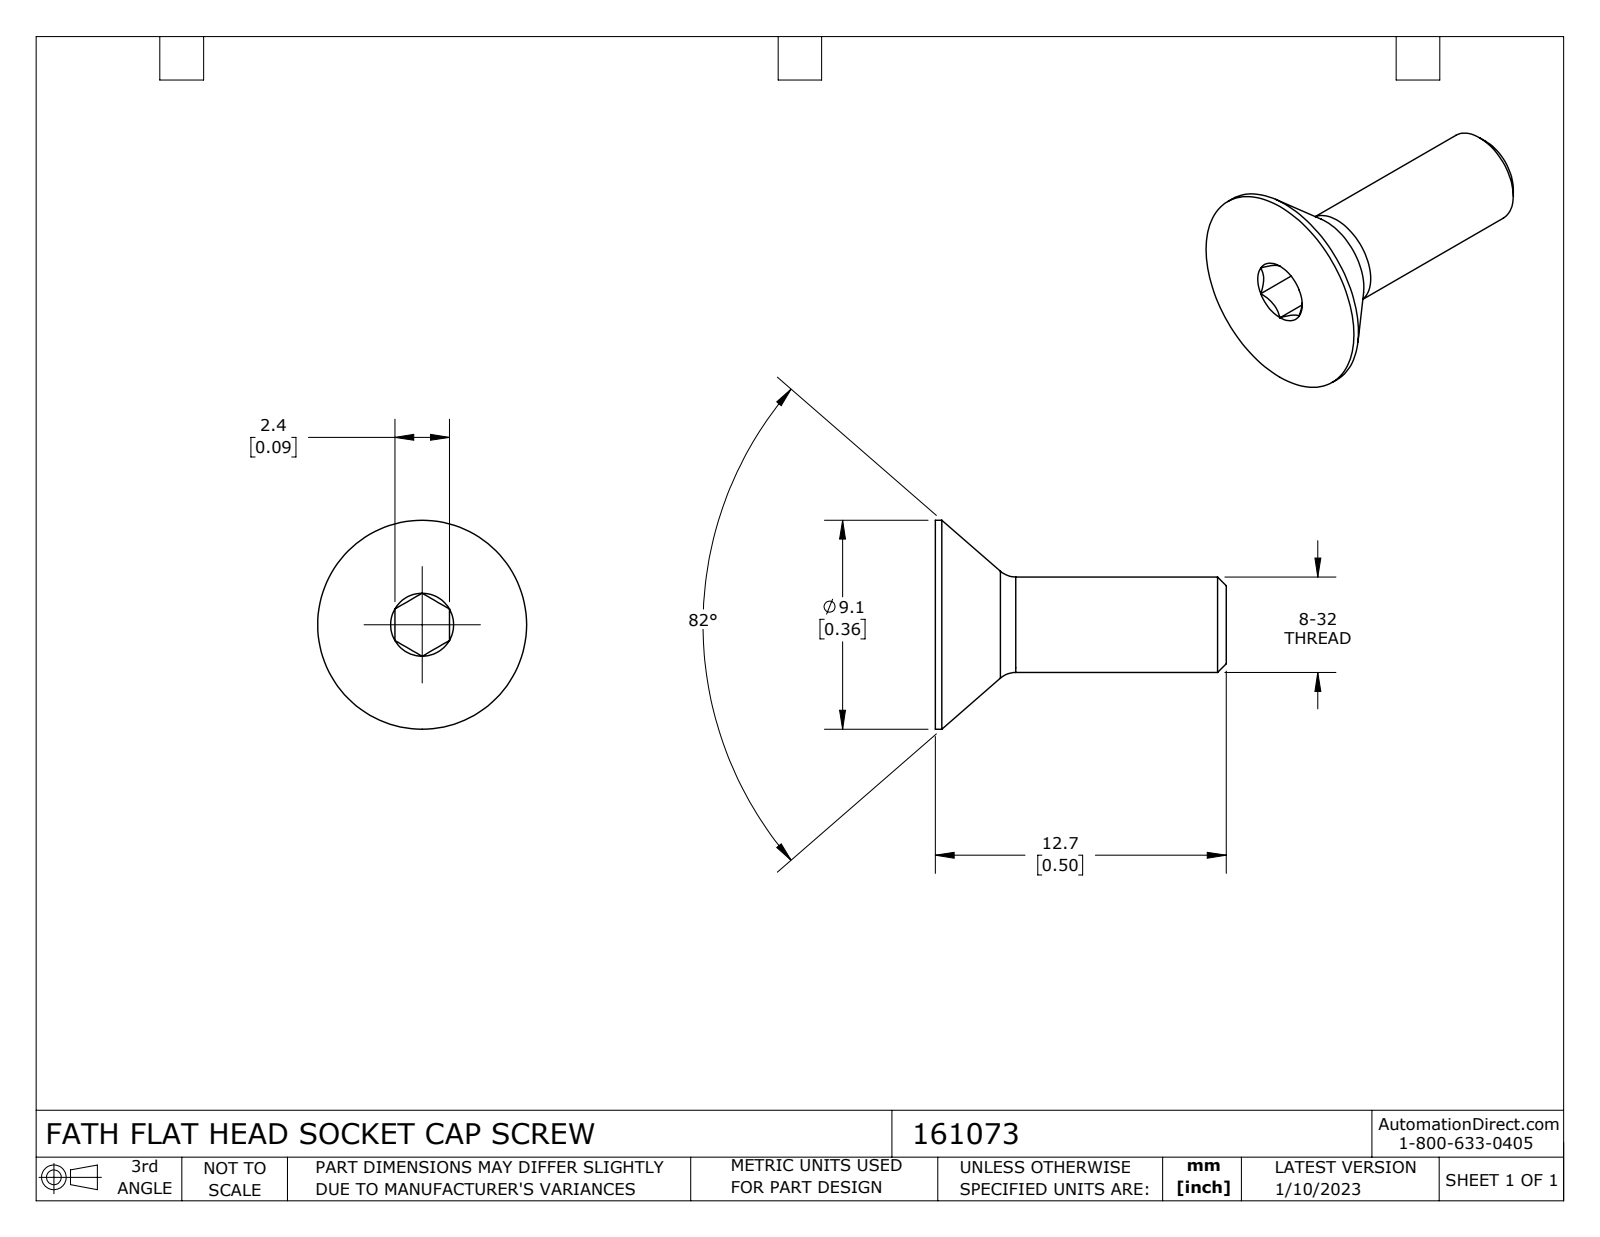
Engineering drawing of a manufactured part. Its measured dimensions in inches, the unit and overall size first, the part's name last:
Units: inches
Overall size (bounding box): 0.5 × 0.359 × 0.359
Round bosses / shafts (diameter × count): ⌀0.359 ×1, ⌀0.164 ×1
Main face-to-face distances: 0.5, 0.094, 0.422, 0.078
Volume: 0.015 in³ · Surface area: 0.47 in²
Bodies: 1 solid, 26 faces (9 planar, 4 cylindrical, 13 other)
Part name (STEP PRODUCT): 161073
STEP written by: SolidWorks 2021 (CONFIG_CONTROL_DESIGN)
